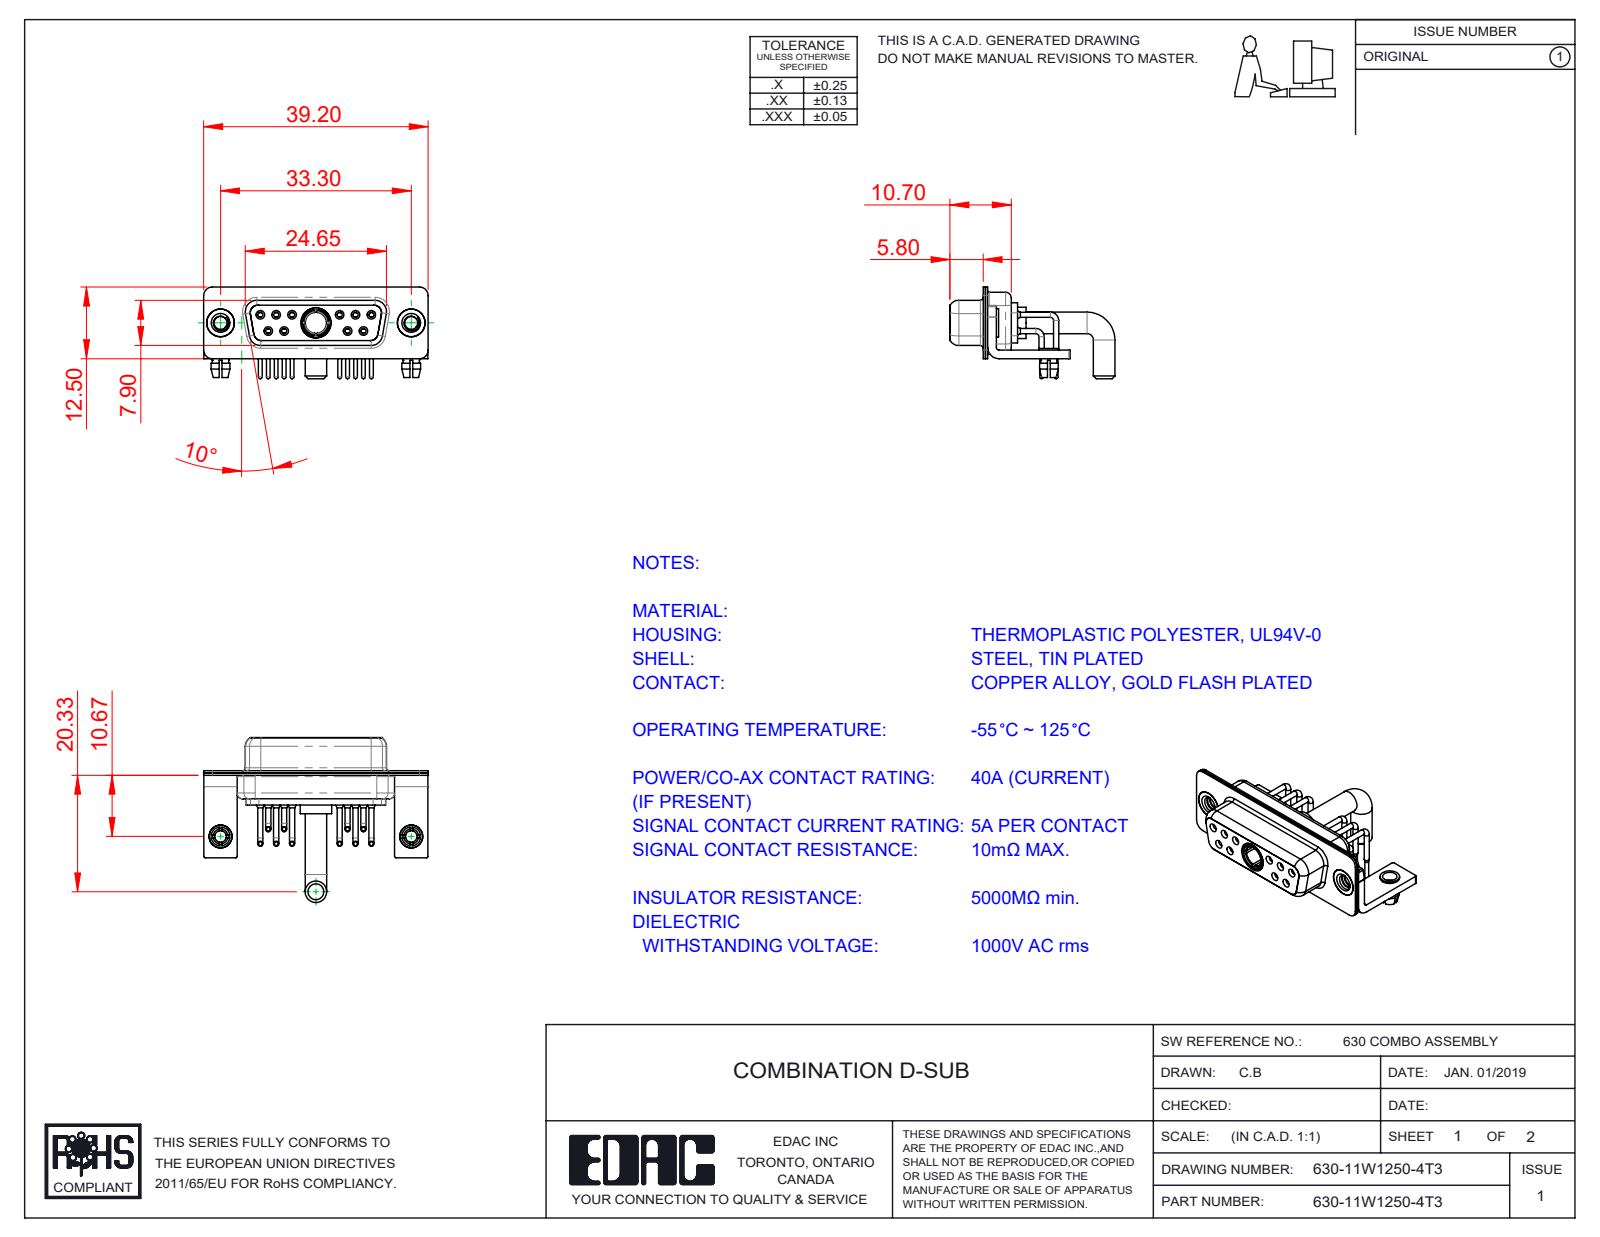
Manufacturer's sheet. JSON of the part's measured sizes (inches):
{"part_name": "630Combo Housing_11W1; 630Combo Board Lock; 630Combo Stabilizer Bracket; 630Combo Contact Row 2 (+6 more)", "step_written_by": "SolidWorks 2020 (CONFIG_CONTROL_DESIGN)", "units": "inches", "bodies": {"solids": 21, "faces": 1019, "planar": 314, "cylindrical": 442, "other": 263}, "overall_size": [1.543, 1.134, 0.63], "volume_in3": 0.189, "surface_area_in2": 11.16, "round_holes": [[0.079, 12], [0.035, 10], [0.043, 10], [0.059, 10], [0.067, 6], [0.063, 4], [0.191, 3], [0.089, 2], [0.098, 2], [0.126, 2], [0.157, 2], [0.159, 2]], "round_bosses_or_shafts": [[0.035, 10], [0.026, 10], [0.063, 6], [0.197, 2], [0.195, 2], [0.189, 2], [0.157, 2], [0.148, 2]], "partial_cylinders_radius": [[0.01, 16], [0.059, 16], [0.079, 13], [0.053, 12], [0.063, 8], [0.02, 5], [0.024, 4], [0.026, 4]], "face_to_face_distances": [0.016, 0.031, 0.018, 0.055, 0.333, 0.071, 0.059, 0.35, 0.244, 0.091], "hole_center_spacings": [0.124, 0.109, 0.545, 0.436, 0.654, 0.198, 0.198, 0.218]}
